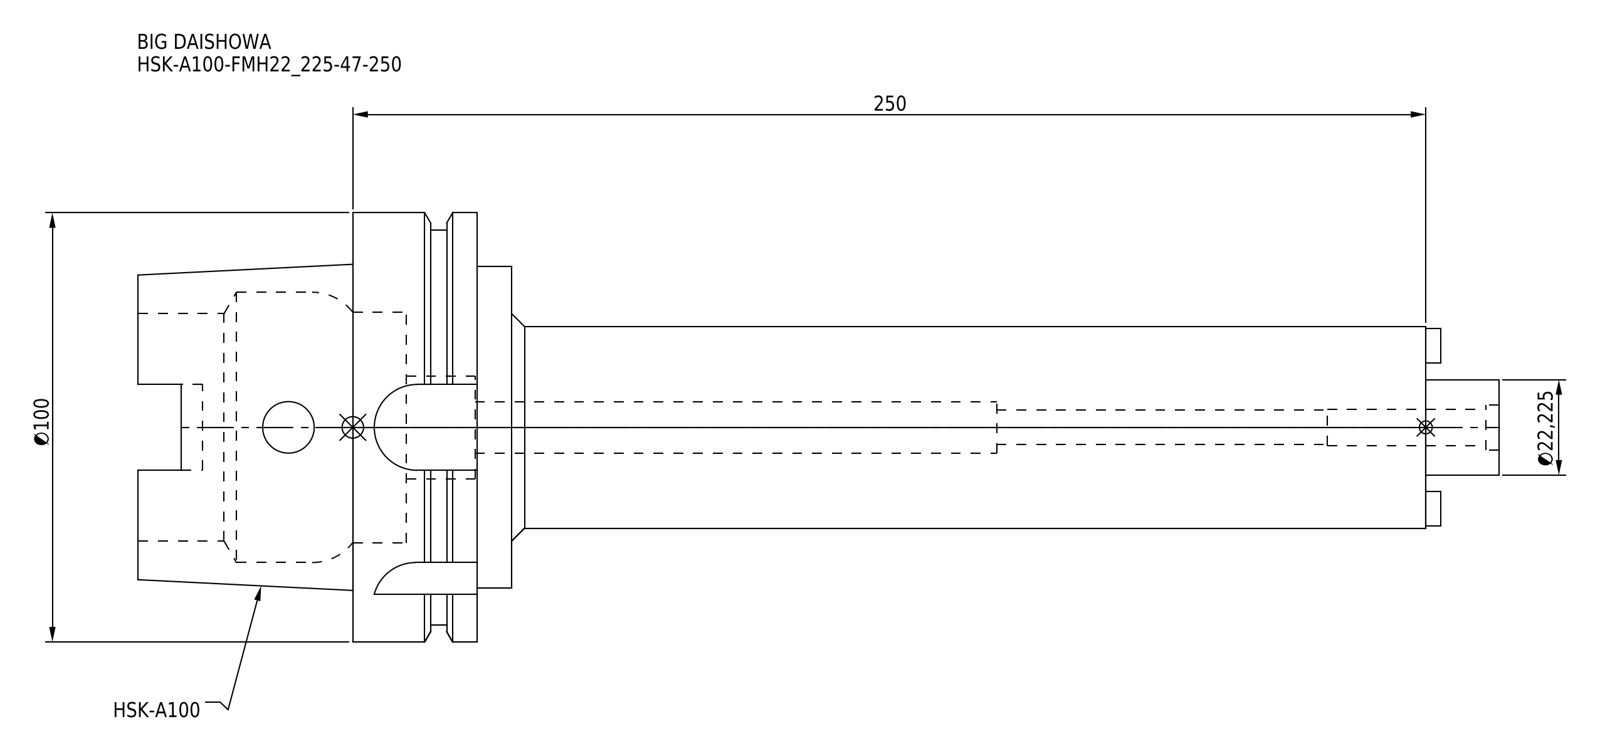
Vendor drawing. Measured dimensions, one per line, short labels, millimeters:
name: HSK-A100-FMH22_225-47-250
written by: CREO PARAMETRIC BY PTC INC, 2016380 (AUTOMOTIVE_DESIGN)
unit: mm
bodies: 1 solid, 109 faces (47 planar, 46 cylindrical, 16 other)
size: 317 × 100 × 100
volume: 646 149 mm³; area: 91 997 mm²
holes: 2× ⌀12, 1× ⌀8, 1× ⌀8.5, 1× ⌀10.5, 1× ⌀24, 1× ⌀53, 1× ⌀53.8, 1× ⌀63
bosses: 1× ⌀100, 1× ⌀92, 1× ⌀75, 1× ⌀47, 1× ⌀22.23
rounds: 4× R4.88, 4× R10
face distances: 29, 8, 37, 24.55, 16.55, 12.45, 213, 221, 237.55, 250
